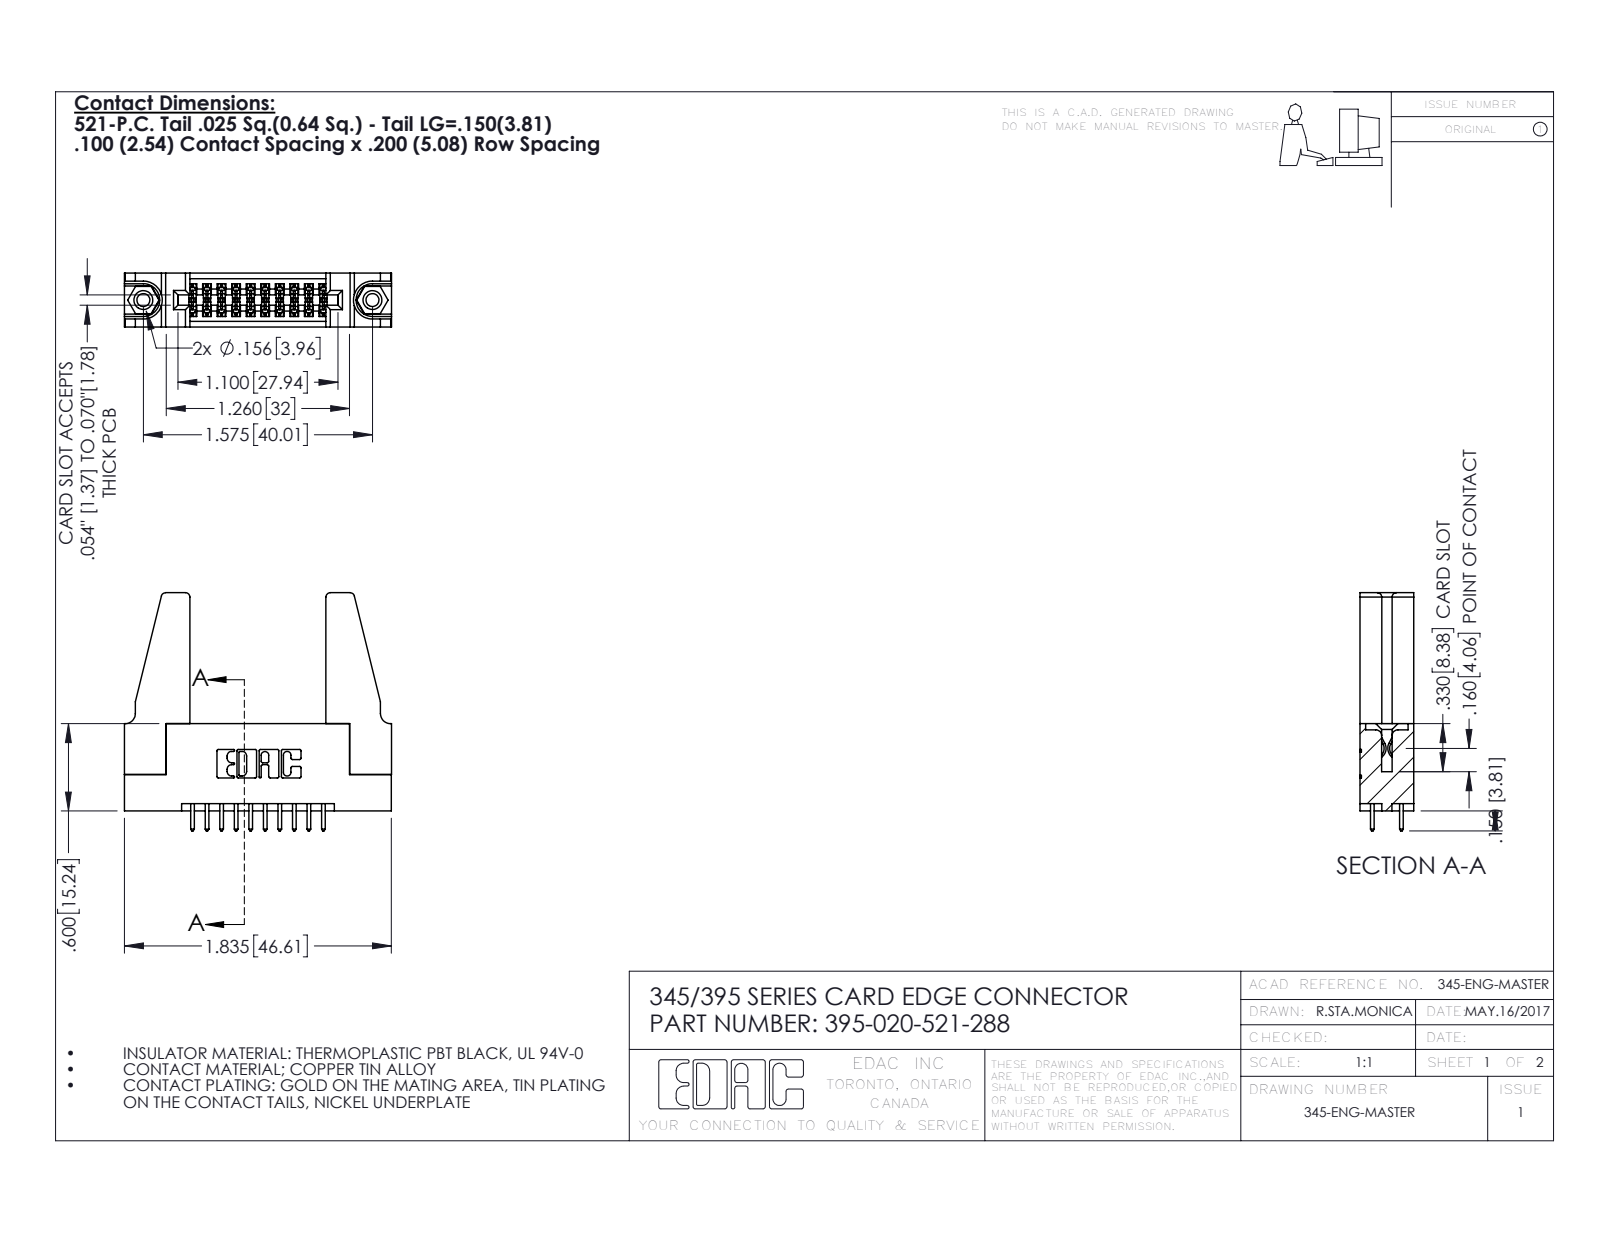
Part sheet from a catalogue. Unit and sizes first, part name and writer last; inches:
Units: inches
Overall size (bounding box): 1.836 × 1.637 × 0.37
Round holes (diameter × count): ⌀0.089 ×2, ⌀0.125 ×2, ⌀0.156 ×2, ⌀0.064 ×1
Round bosses / shafts (diameter × count): ⌀0.155 ×2
Partial cylindrical surfaces — rounded edges, fillets, slot ends (radius × count): R0.006 ×30, R0.01 ×22, R0.01 ×20, R0.03 ×8, R0.007 ×6, R0.031 ×6, R0.026 ×3, R0.014 ×2
Main face-to-face distances: 0.37, 0.072, 0.298, 0.2, 0.098, 0.272, 0.025, 0.225, 0.148, 0.15
Hole centre spacings: 0.27, 1.344, 1.575
Volume: 0.456 in³ · Surface area: 13.48 in²
Bodies: 25 solids, 1250 faces (812 planar, 422 cylindrical, 16 other)
Part name (STEP PRODUCT): 395-020-521-288; 345-250-001_345-250-001-102; 345-292-001_345-293-121; 345-220-078_345-220-088 (+1 more)
STEP written by: SolidWorks 2016 (CONFIG_CONTROL_DESIGN)
